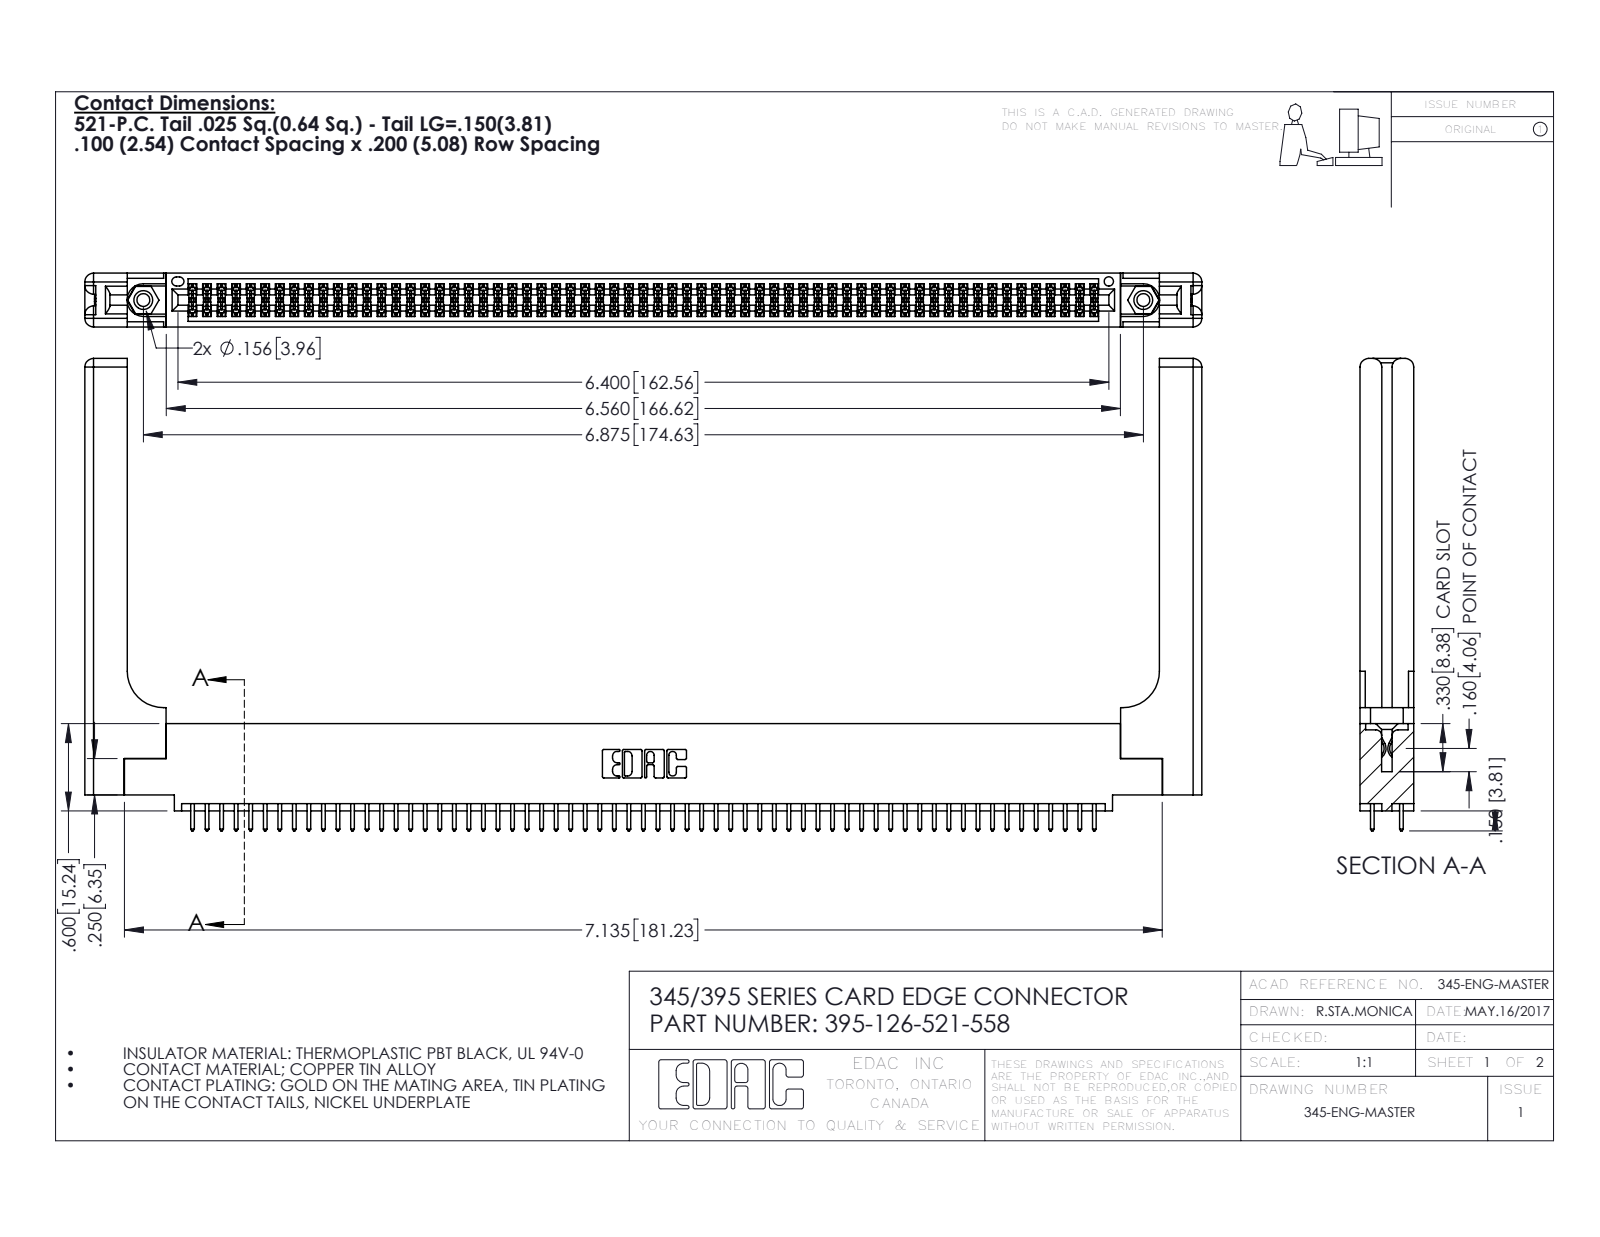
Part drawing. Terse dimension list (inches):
name: 345-250-001_345-250-001-102; 395-126-521-558; 345 Part_0.110 Offset - 0.156 Dia-TH; 345-292-001_345-293-121 (+1 more)
written by: SolidWorks 2016 (CONFIG_CONTROL_DESIGN)
unit: in
bodies: 131 solids, 6686 faces (4390 planar, 2236 cylindrical, 60 other)
size: 7.679 × 3.247 × 0.37
volume: 1.678 in³; area: 51.67 in²
holes: 2× ⌀0.089, 2× ⌀0.125, 2× ⌀0.156, 1× ⌀0.064
bosses: 2× ⌀0.155
rounds: 189× R0.006, 126× R0.01, 22× R0.01, 16× R0.06, 6× R0.007, 6× R0.031, 3× R0.026, 2× R0.014
face distances: 0.072, 0.298, 0.37, 0.098, 0.272, 0.025, 0.2, 0.225, 0.175, 0.148
hole spacings: 0.27, 6.639, 6.875
